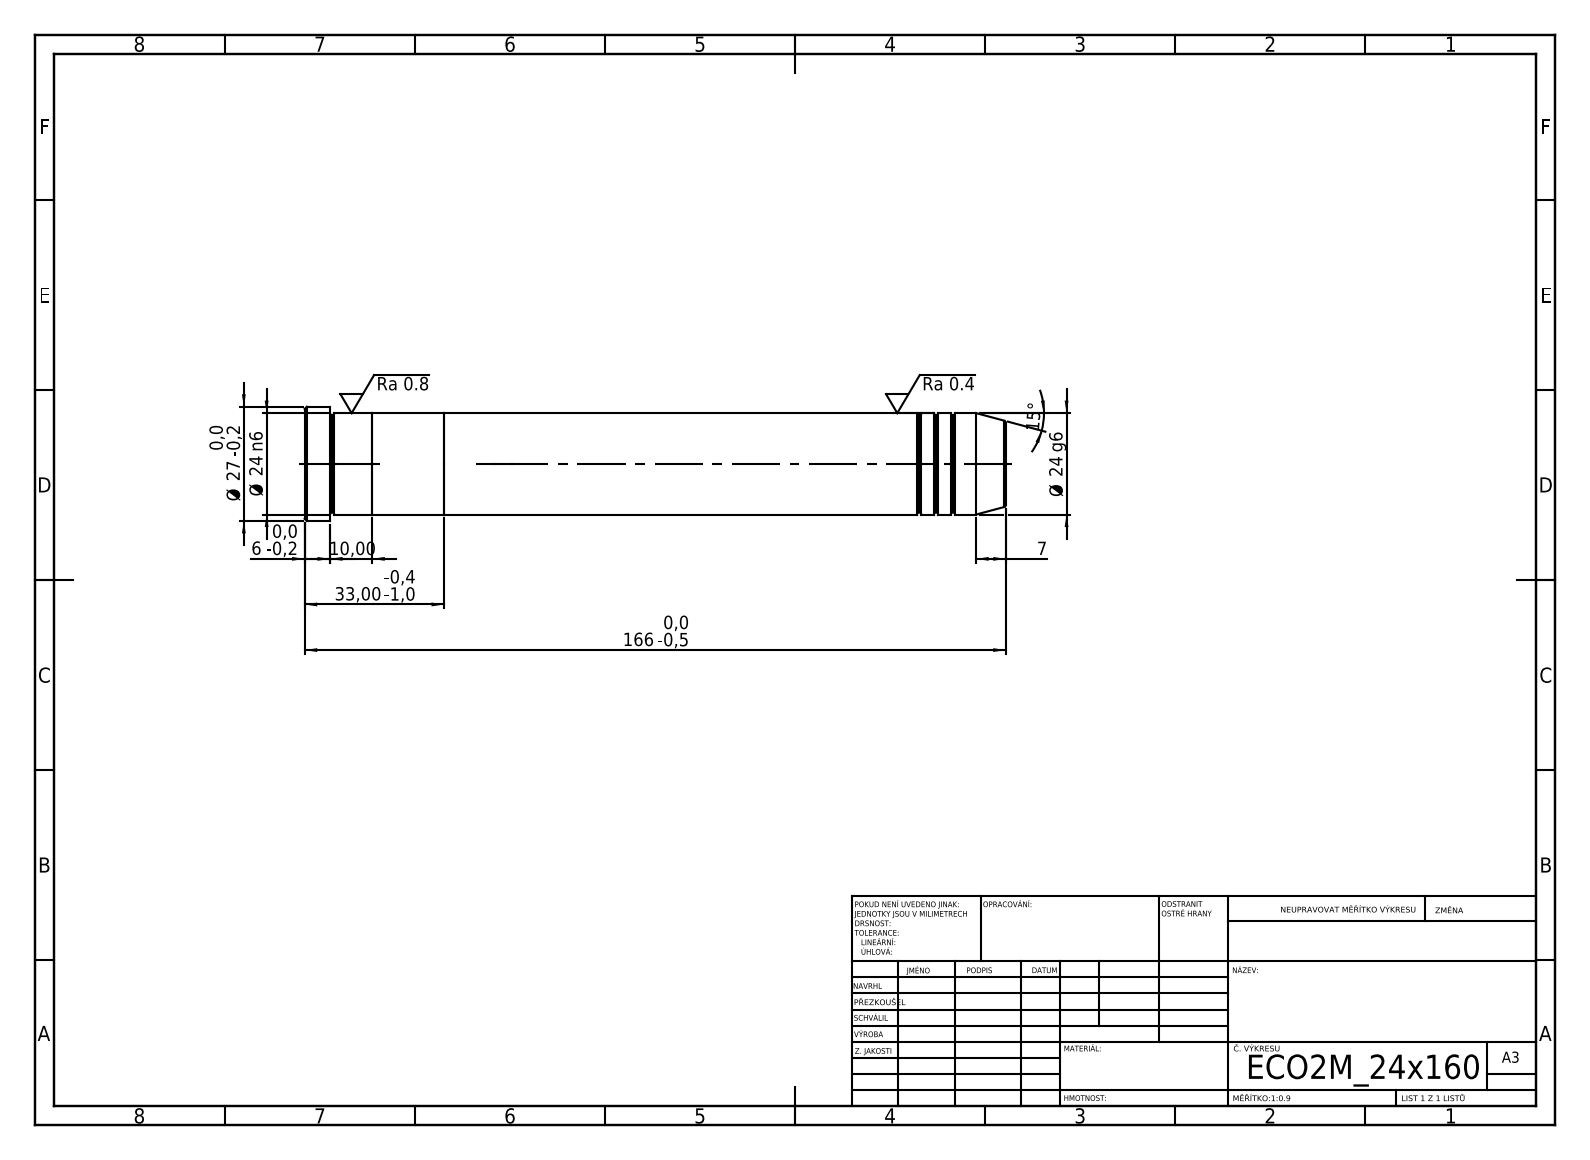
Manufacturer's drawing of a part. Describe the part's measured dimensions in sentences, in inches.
Its 3-D file was written by "SolidWorks 2019 (CONFIG_CONTROL_DESIGN)". It is 3 solids with 43 faces: 7 planar, 14 cylindrical and 22 other. Overall it measures 6.535 by 1.063 by 1.063 inches. Its volume is 4.59 cubic inches and its surface area 24.03 square inches. Round bosses or shafts: 1 of diameter 1.063, 1 of diameter 0.945. The main face-to-face distances are 0.669, 1.299, 0.63, 5.236, 5.906, 6.535, 6.299, 1.063, 0.394, 0.236.
